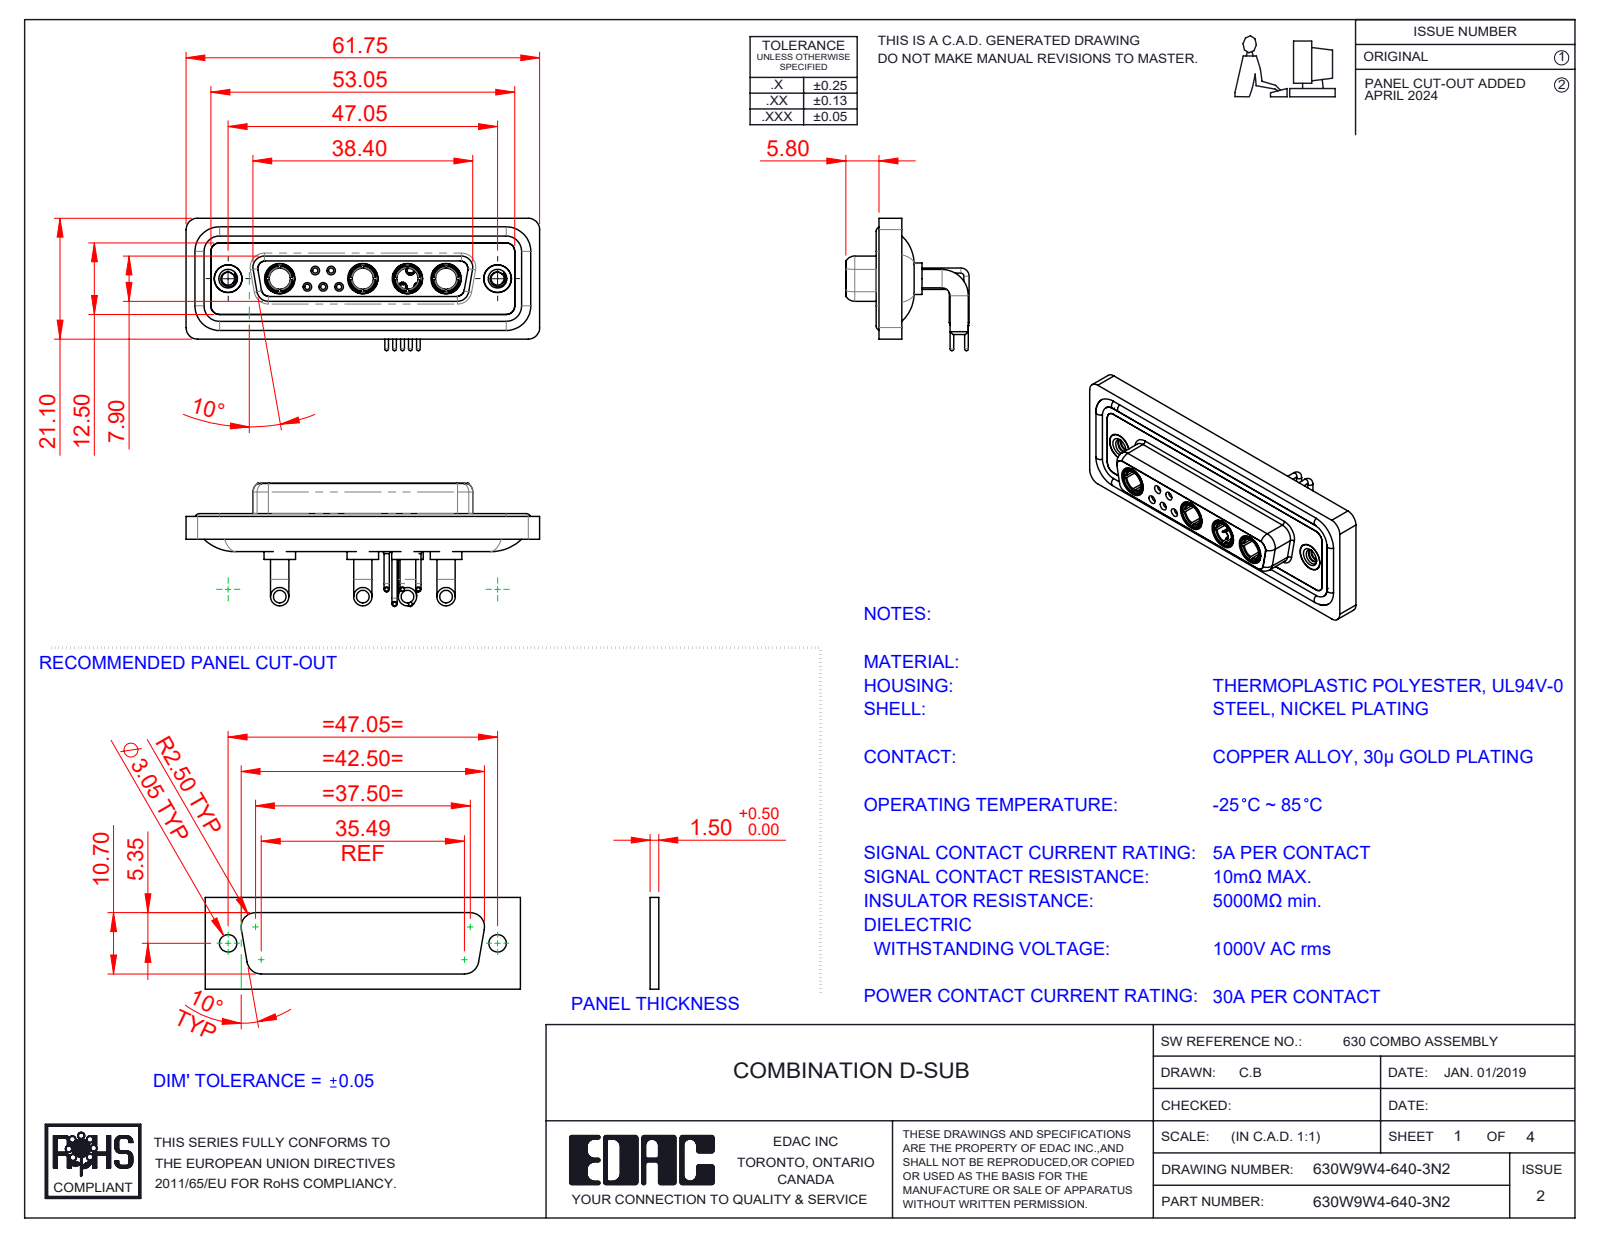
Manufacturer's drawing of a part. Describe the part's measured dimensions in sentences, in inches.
The part is named "630W9W4-640-3N2; 630Combo Contact Row 1_50 Contacts; 630Combo Shell Front_25 Contacts; 630Combo Housing_9W4 (+5 more)". Its 3-D file was written by "SolidWorks 2023 (CONFIG_CONTROL_DESIGN)". It is 20 solids with 963 faces: 296 planar, 403 cylindrical and 264 other. Overall it measures 2.431 by 0.91 by 0.848 inches. Its volume is 0.523 cubic inches and its surface area 21.89 square inches. Round holes: 6 of diameter 0.191, 5 of diameter 0.035, 5 of diameter 0.043, 5 of diameter 0.059, 5 of diameter 0.079, 4 of diameter 0.146, 4 of diameter 0.209, 3 of diameter 0.063, 2 of diameter 0.067, 2 of diameter 0.089, 2 of diameter 0.157, 2 of diameter 0.159. Round bosses or shafts: 10 of diameter 0.035, 9 of diameter 0.063, 8 of diameter 0.126, 5 of diameter 0.079, 5 of diameter 0.059, 5 of diameter 0.026, 4 of diameter 0.217, 4 of diameter 0.205. Partial cylindrical surfaces (rounded edges, fillets, slot ends): 18 of radius 0.059, 18 of radius 0.079, 8 of radius 0.053, 8 of radius 0.063, 4 of radius 0.01, 4 of radius 0.02, 4 of radius 0.024, 4 of radius 0.026. The main face-to-face distances are 0.016, 0.071, 0.161, 0.043, 0.063, 0.059, 0.098, 0.122, 0.146, 0.055. The hole center spacings are 0.124, 0.109, 0.198, 0.545, 0.436, 0.504, 0.61, 0.218.
